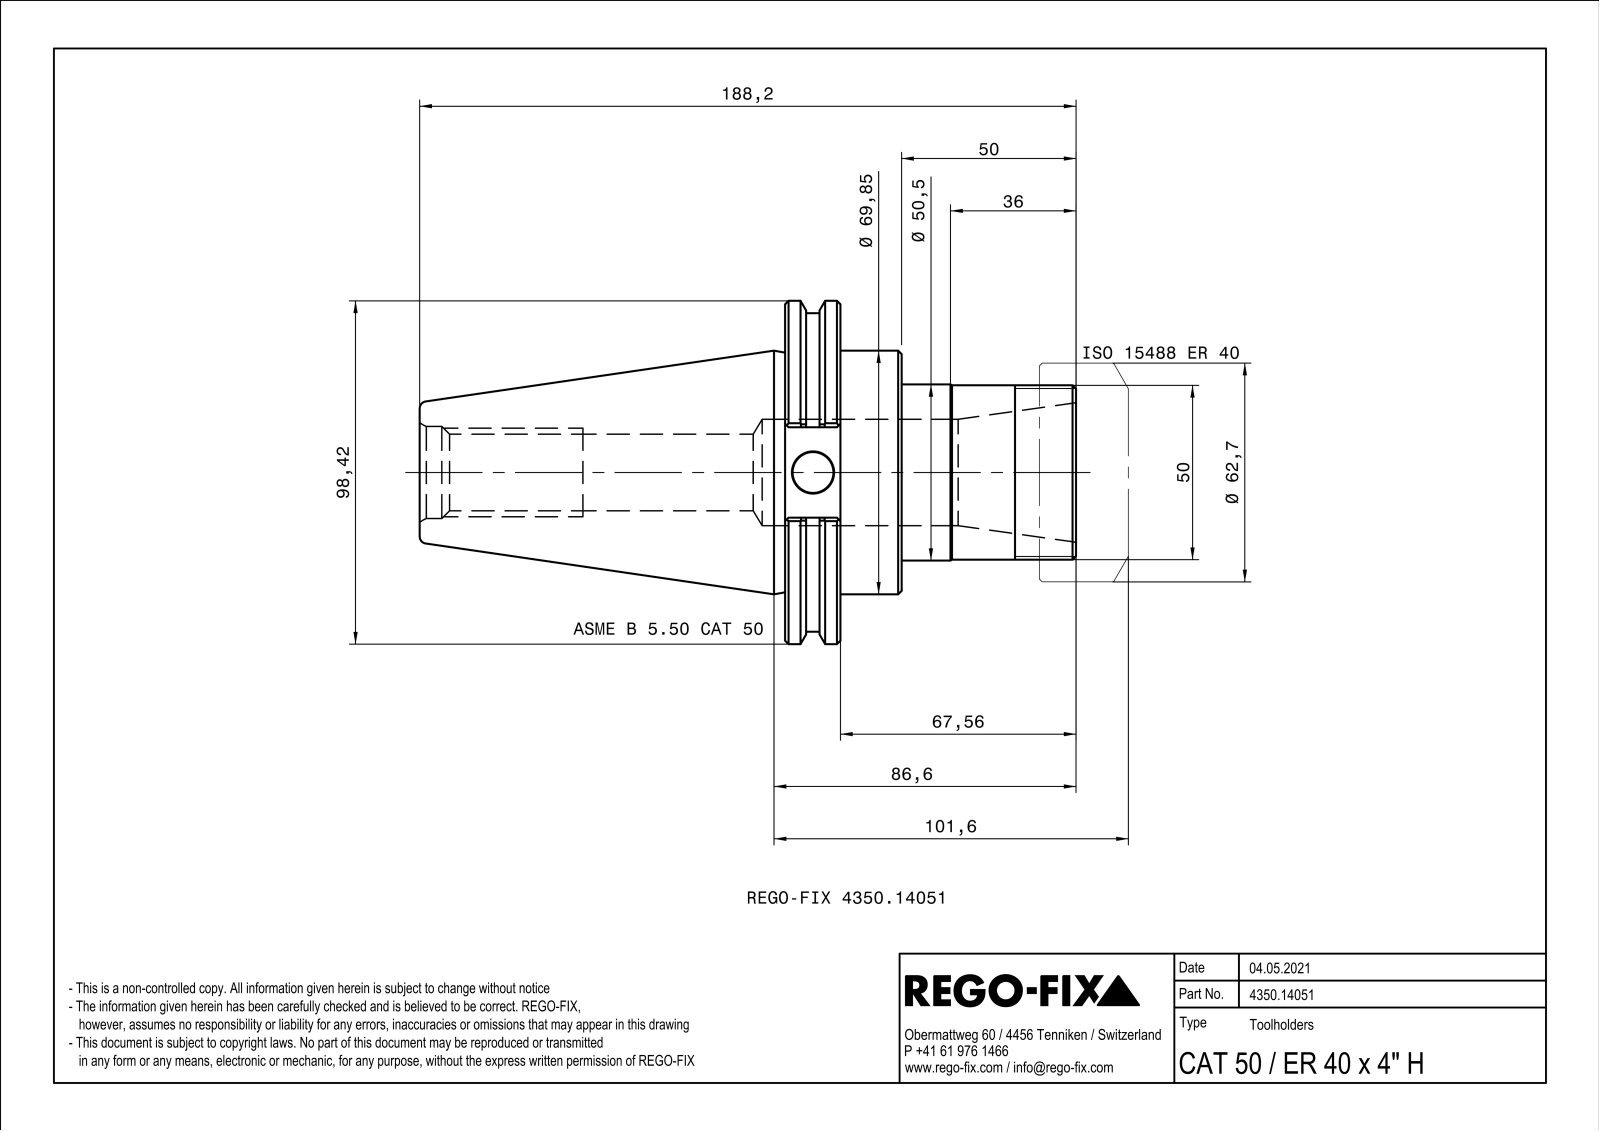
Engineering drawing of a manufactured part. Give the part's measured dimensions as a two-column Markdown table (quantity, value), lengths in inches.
| quantity | value |
| --- | --- |
| part name | NOCUT |
| STEP written by | SIEMENS PLM Software Solid Edge ST10 (AUTOMOTIVE_DESIGN) |
| units | inches |
| bodies | 1 solid, 110 faces (32 planar, 31 cylindrical, 47 other) |
| overall size | 7.409 × 3.875 × 3.716 |
| volume | 25.41 in³ |
| surface area | 96.57 in² |
| round holes (diameter × count) | 0.461 × 1, 0.865 × 1, 0.865 × 1, 1.039 × 1, 1.201 × 1 |
| round bosses / shafts (diameter × count) | 3.875 × 1, 3.594 × 1, 2.75 × 1, 1.988 × 1, 1.969 × 1 |
| partial cylindrical surfaces (radius × count) | 0.02 × 12 |
| main face-to-face distances | 0.625, 0.691, 1.316, 1.969, 2.66, 3.285, 7.409, 5.441, 4.75, 4.125 |
